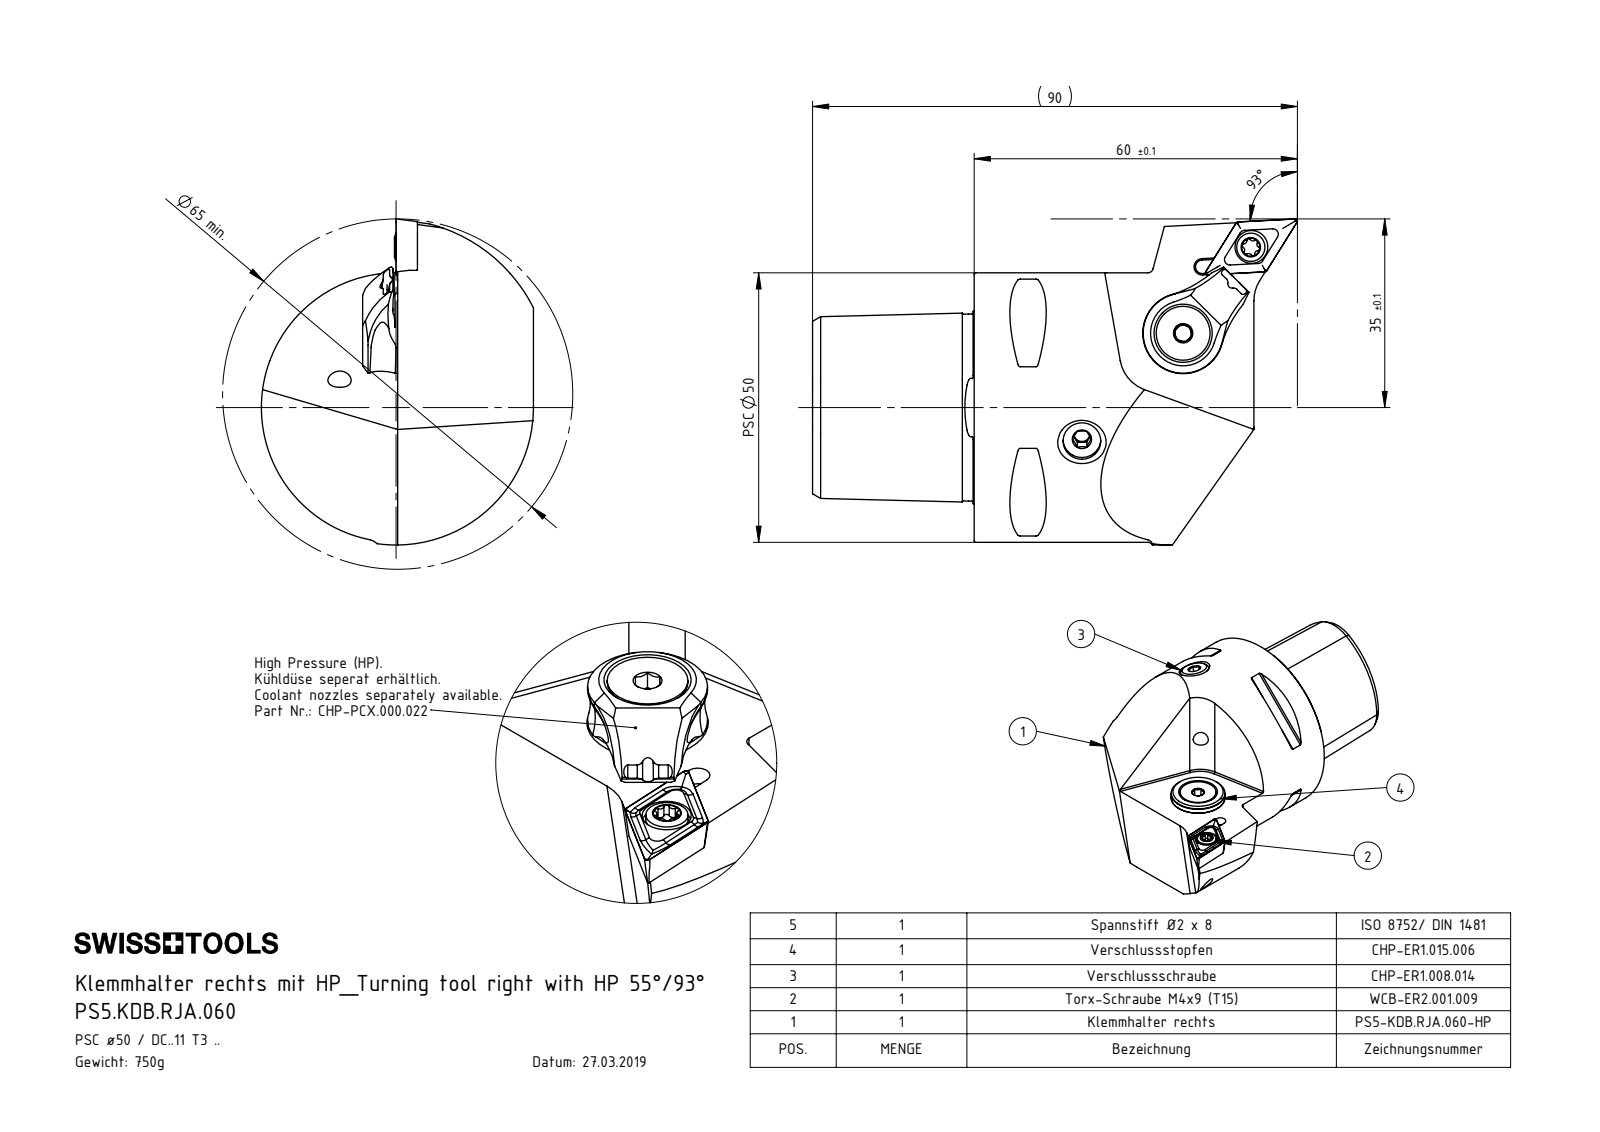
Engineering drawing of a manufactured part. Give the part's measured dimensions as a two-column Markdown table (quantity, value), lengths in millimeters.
| quantity | value |
| --- | --- |
| part name | PS5-KDB.RJA.060; KVT_MB_600_060; DCMT11T304; WCB-ER2.001.009_A (+1 more) |
| STEP written by | SolidWorks 2012 (CONFIG_CONTROL_DESIGN) |
| units | millimeters |
| bodies | 5 solids, 269 faces (51 planar, 67 cylindrical, 151 other) |
| overall size | 90.01 × 60 × 50.5 |
| volume | 87 446 mm³ |
| surface area | 18 908 mm² |
| round holes (diameter × count) | 5 × 3, 6.1 × 2, 3.3 × 1, 4 × 1, 4.4 × 1, 6 × 1, 14.5 × 1, 21 × 1, 24 × 1 |
| round bosses / shafts (diameter × count) | 50 × 1, 6 × 1, 5.25 × 1, 4 × 1 |
| partial cylindrical surfaces (radius × count) | 0.5 × 8, 0.34 × 6, 0.59 × 6, 1.25 × 1, 3 × 1, 4 × 1, 25.5 × 1, 26 × 1 |
| main face-to-face distances | 30, 25.2, 19.18, 21.53, 3.67, 44.4, 20, 10, 29.8, 9.8 |
| hole center spacings | 26, 49.32, 49.45, 71.8, 71.92 |
